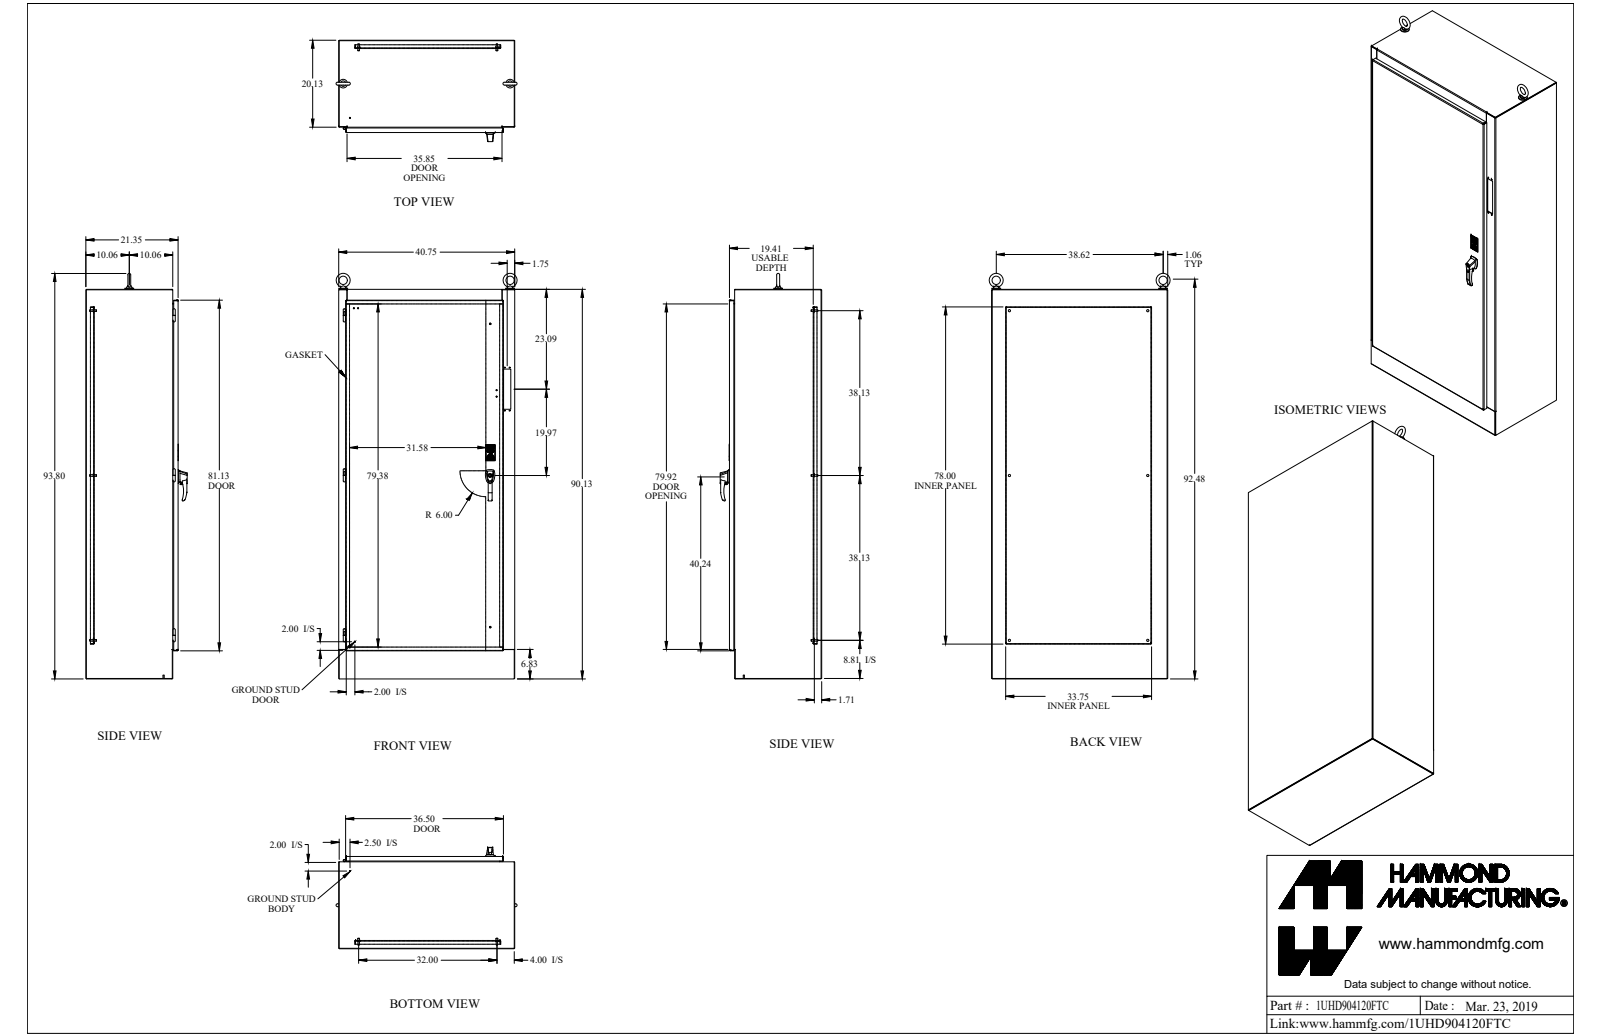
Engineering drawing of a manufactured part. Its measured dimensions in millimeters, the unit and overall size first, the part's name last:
Units: millimetres
Overall size (bounding box): 2382.5 × 1063.5 × 596
Round holes (diameter × count): ⌀7.8 ×7, ⌀8.9 ×7, ⌀7.1 ×6, ⌀11.3 ×6, ⌀14.3 ×6, ⌀5 ×5, ⌀6.4 ×3, ⌀8 ×3, ⌀4.2 ×2, ⌀6.5 ×2, ⌀6.5 ×2, ⌀7.1 ×2
Round bosses / shafts (diameter × count): ⌀6.4 ×10, ⌀25.4 ×8, ⌀9.5 ×7, ⌀16.5 ×6, ⌀8.4 ×6, ⌀7.1 ×4, ⌀4.8 ×4, ⌀15.9 ×3
Partial cylindrical surfaces — rounded edges, fillets, slot ends (radius × count): R1.5 ×39, R4.7 ×28, R12.7 ×25, R3.2 ×22, R0.4 ×16, R0.8 ×12, R3.3 ×8, R19.1 ×7
Main face-to-face distances: 3.2, 539.1, 3.2, 535.9, 542.3, 49.2, 46, 489.9, 493.1, 46
Hole centre spacings: 812.8, 25.4, 28.6, 28.6, 32.7, 50.8, 188.8, 189.6
Volume: 36 020 000 mm³ · Surface area: 22 720 000 mm²
Bodies: 102 solids, 1773 faces (978 planar, 482 cylindrical, 313 other)
Part name (STEP PRODUCT): 1UHD904120FTC
STEP written by: SolidWorks 2018 (AUTOMOTIVE_DESIGN)
